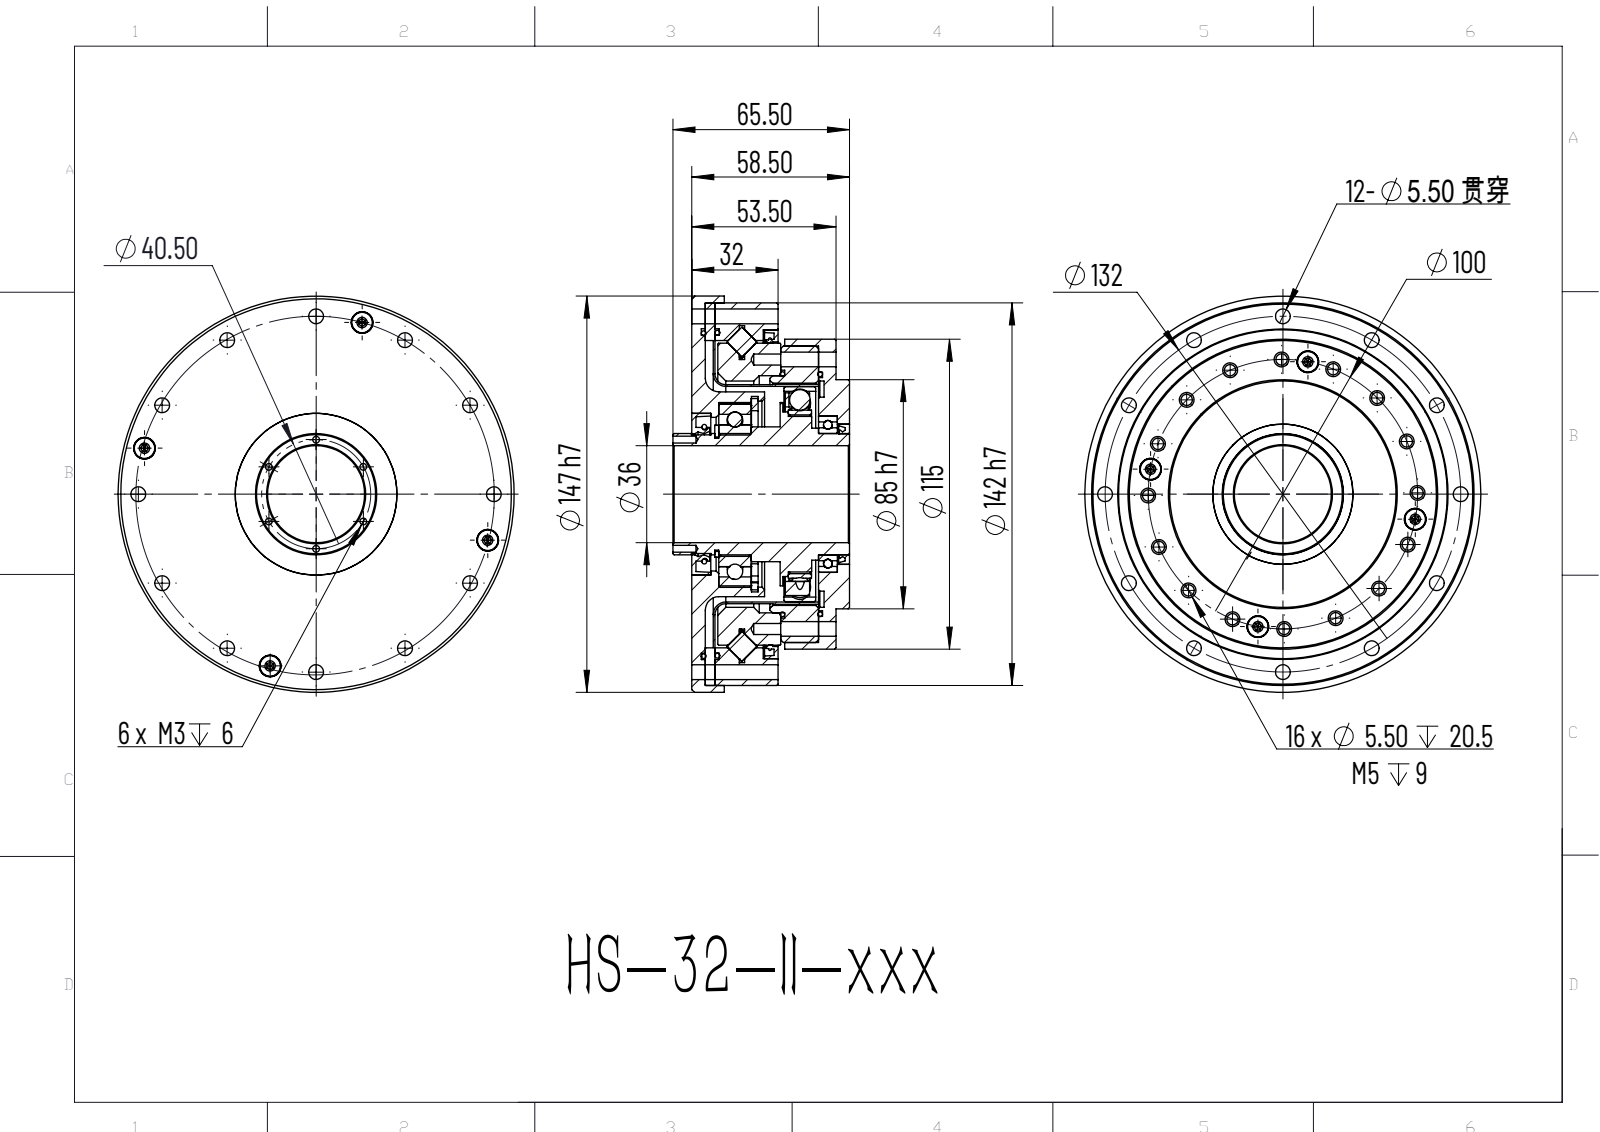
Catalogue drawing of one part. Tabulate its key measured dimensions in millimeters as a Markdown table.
| quantity | value |
| --- | --- |
| part name | HS-32-II; circlips for shaft--type a large gb_GB_CONNECTING_PIECE_RING_RRA 45; hexagon socket button head screws gb_GB_SOCKET_TYPE7 M4X10-C; ??-?45X?60X7 (+8 more) |
| STEP written by | ONSHAPE BY PTC INC, 1.201 (AP242_MANAGED_MODEL_BASED_3D_ENGINEERING_MIM_LF) |
| units | millimeters |
| bodies | 103 solids, 1352 faces (504 planar, 379 cylindrical, 469 other) |
| overall size | 147 × 147 × 65.5 |
| volume | 573 085 mm³ |
| surface area | 328 653 mm² |
| round holes (diameter × count) | 5.5 × 28, 4.2 × 16, 3.3 × 12, 4.5 × 12, 8 × 8, 2.5 × 6, 3 × 4, 45 × 2, 36 × 1, 41.5 × 1, 44.96 × 1, 52 × 1 |
| round bosses / shafts (diameter × count) | 8 × 44, 4 × 8, 7 × 4, 49 × 2, 147 × 1, 142 × 1, 118 × 1, 115 × 1 |
| partial cylindrical surfaces (radius × count) | 0.45 × 32, 4.21 × 21, 2.3 × 4, 0.7 × 2, 1.5 × 2, 2 × 2, 4 × 2, 27.5 × 1 |
| main face-to-face distances | 5, 8.6, 3.6, 42, 1, 23.4, 53.5, 47, 38.4, 32 |
| hole center spacings | 50, 70.71, 83.15, 92.39, 55.56, 38.27, 77.3, 9.8 |
